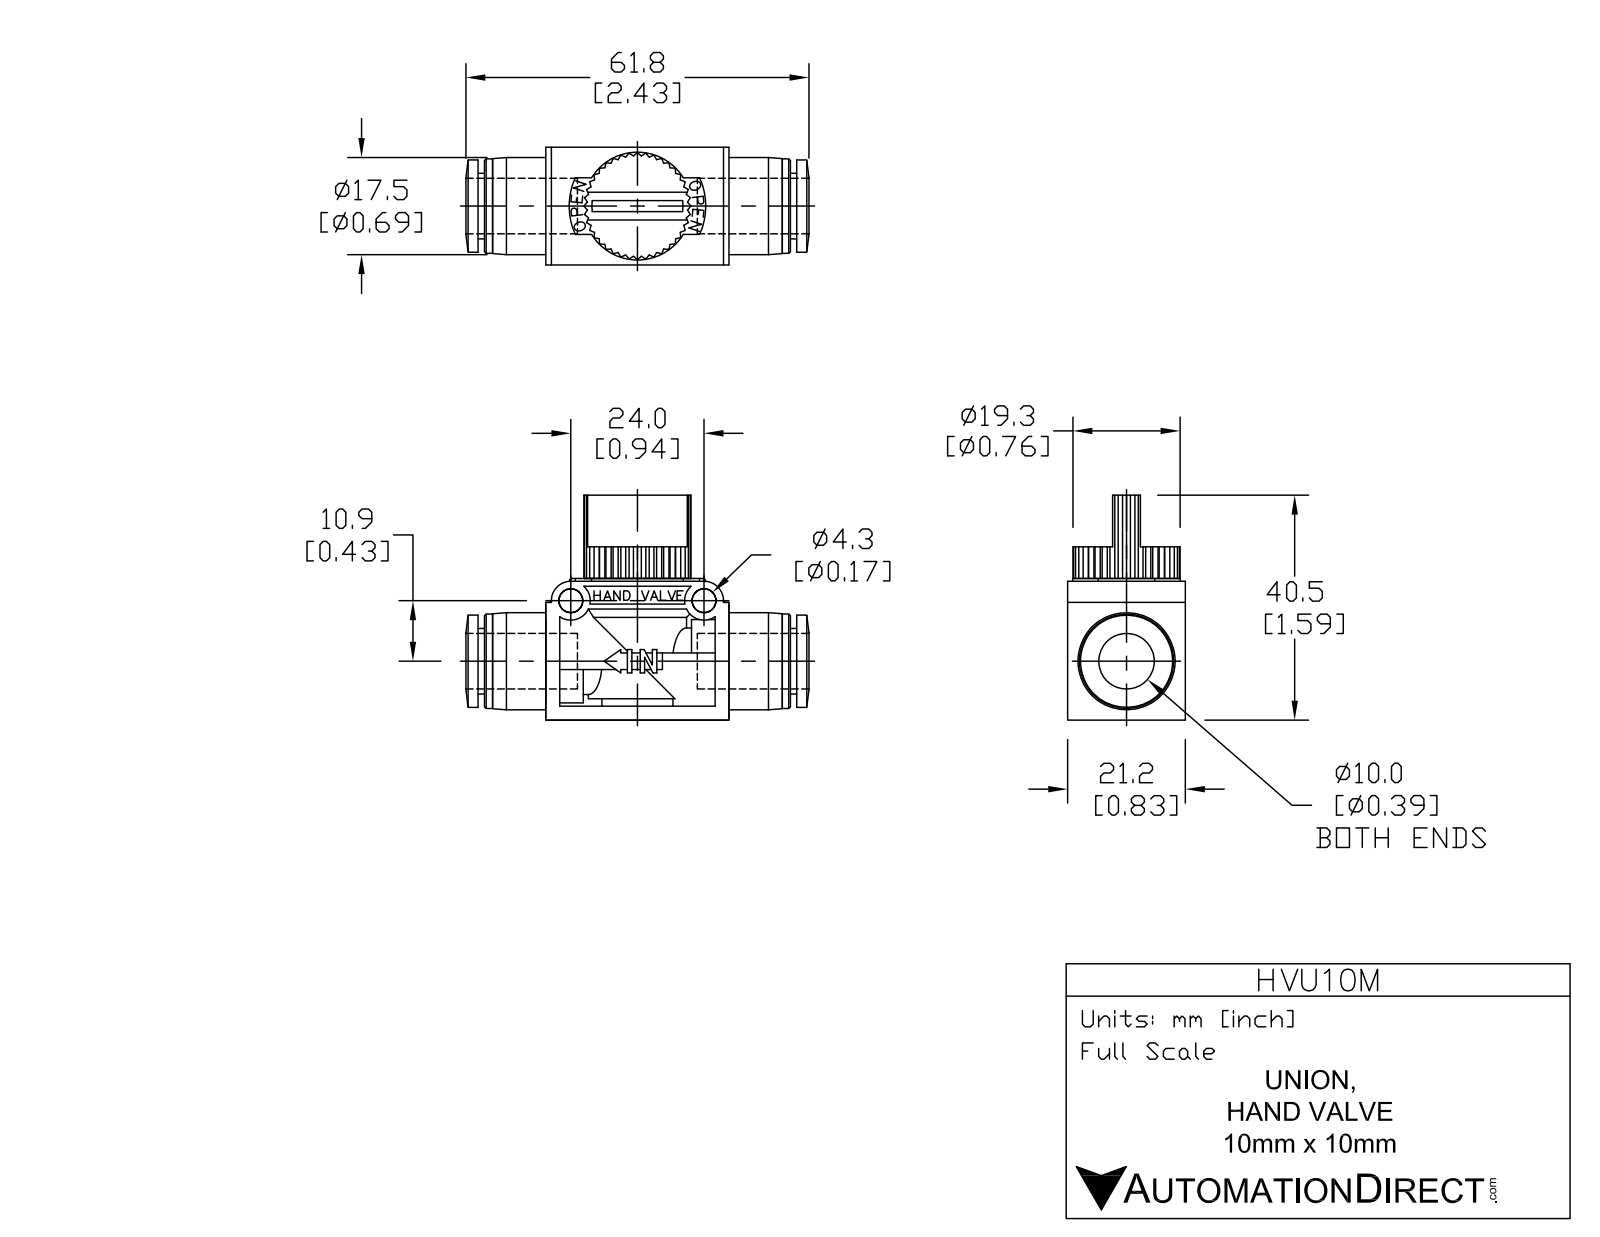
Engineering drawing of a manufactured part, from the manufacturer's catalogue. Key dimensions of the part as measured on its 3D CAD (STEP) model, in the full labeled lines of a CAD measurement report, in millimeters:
Part name (STEP PRODUCT): HVU10M
STEP written by: SolidWorks 2015 (AUTOMOTIVE_DESIGN)
Units: millimetres
Bodies: 1 solid, 301 faces (214 planar, 60 cylindrical, 27 other)
Overall size (bounding box): 61.8 × 40.5 × 21.2
Volume: 18 620 mm³ · Surface area: 10 540 mm²
Round holes (diameter × count): ⌀4.3 ×2, ⌀10.3 ×1
Round bosses / shafts (diameter × count): ⌀17.8 ×1, ⌀17.7 ×1, ⌀17.5 ×1, ⌀17 ×1, ⌀16.6 ×1, ⌀15 ×1, ⌀11.8 ×1
Partial cylindrical surfaces — rounded edges, fillets, slot ends (radius × count): R3.5 ×2, R6.1 ×1, R6.4 ×1, R10.3 ×1
Main face-to-face distances: 2.5, 8.1, 13.1, 1.5, 9.6, 11.6, 21.2, 3.5, 30.5, 14.5
Hole centre spacings: 24
